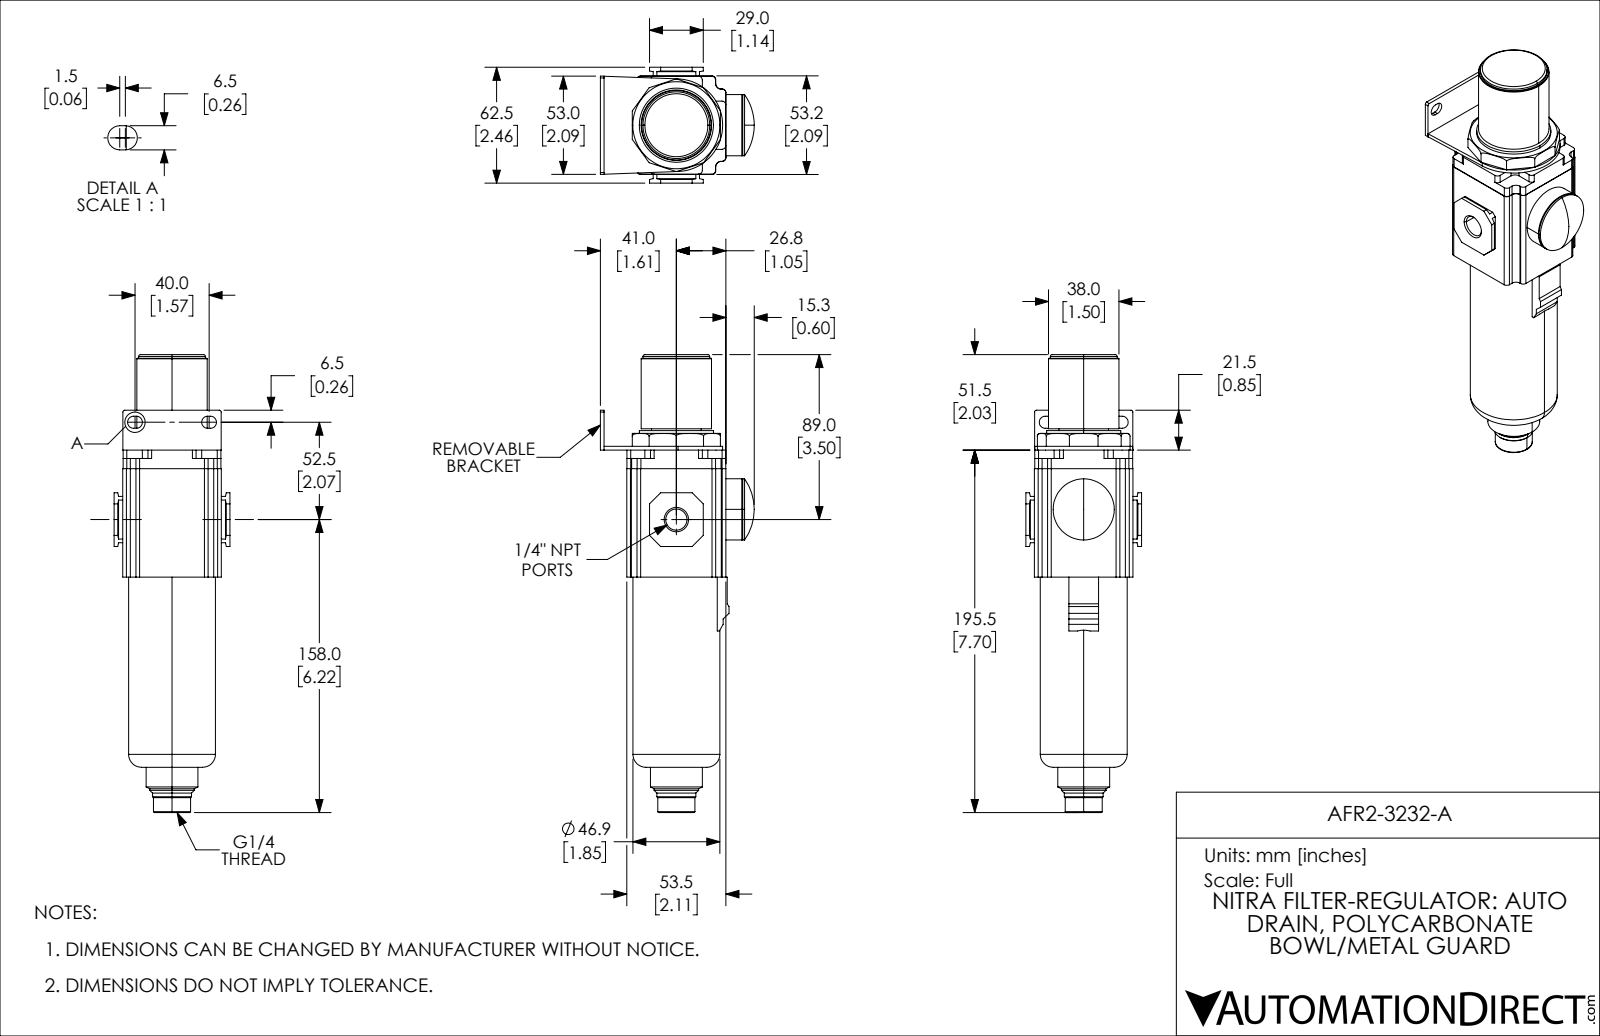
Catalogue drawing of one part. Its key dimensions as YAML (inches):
part_name: "AFR2-3232-A"
step_written_by: "SolidWorks 2019 (CONFIG_CONTROL_DESIGN)"
units: inches
bodies: {solids: 1, faces: 221, planar: 124, cylindrical: 71, other: 26}
overall_size: [9.724, 3.269, 2.461]
volume: 27.63
surface_area: 80.03
round_holes:
  - {diameter: 0.451, count: 2}
round_bosses_or_shafts:
  - {diameter: 1.846, count: 1}
  - {diameter: 1.575, count: 1}
  - {diameter: 1.496, count: 1}
  - {diameter: 1.417, count: 1}
  - {diameter: 1.299, count: 1}
  - {diameter: 1.102, count: 1}
  - {diameter: 1.054, count: 1}
  - {diameter: 0.945, count: 1}
partial_cylinders:
  - {radius: 0.079, count: 24}
  - {radius: 0.118, count: 12}
  - {radius: 0.128, count: 4}
  - {radius: 0.039, count: 2}
  - {radius: 0.984, count: 1}
face_to_face_distances: [0.079, 2.094, 2.106, 0.183, 2.278, 0.561, 0.482, 2.667, 2.028, 1.949]
